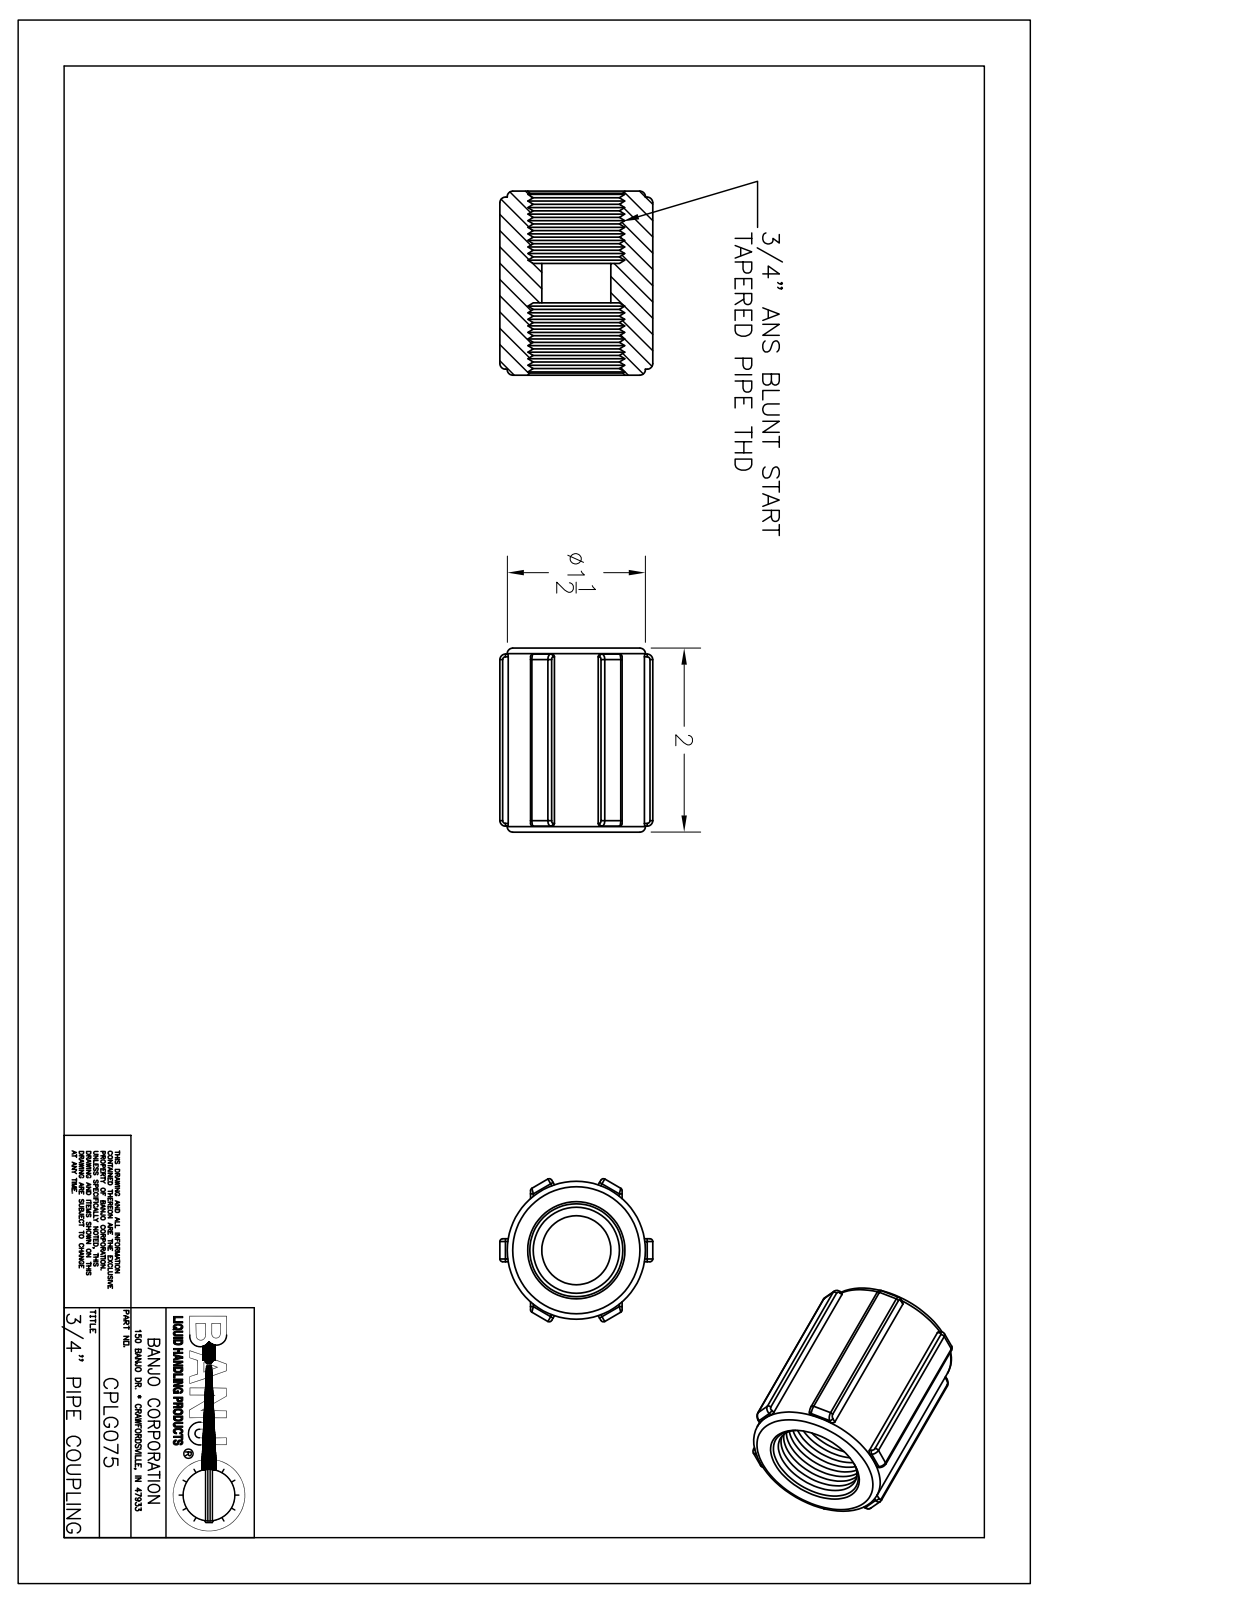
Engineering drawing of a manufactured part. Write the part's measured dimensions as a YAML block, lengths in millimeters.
part_name: "CPLG075U"
step_written_by: "Autodesk Inventor 2014 (AUTOMOTIVE_DESIGN)"
units: millimeters
bodies: {solids: 1, faces: 577, planar: 183, cylindrical: 70, other: 324}
overall_size: [50.8, 42.67, 39.57]
volume: 39137
surface_area: 14370
round_holes:
  - {diameter: 19.05, count: 1}
partial_cylinders:
  - {radius: 0.76, count: 24}
  - {radius: 7.93, count: 1}
  - {radius: 18.8, count: 1}
  - {radius: 19.05, count: 1}
face_to_face_distances: [42.68, 7.92, 34.76, 20.07, 30.73, 50.8, 26.84, 10.66, 6.36, 6.34]
